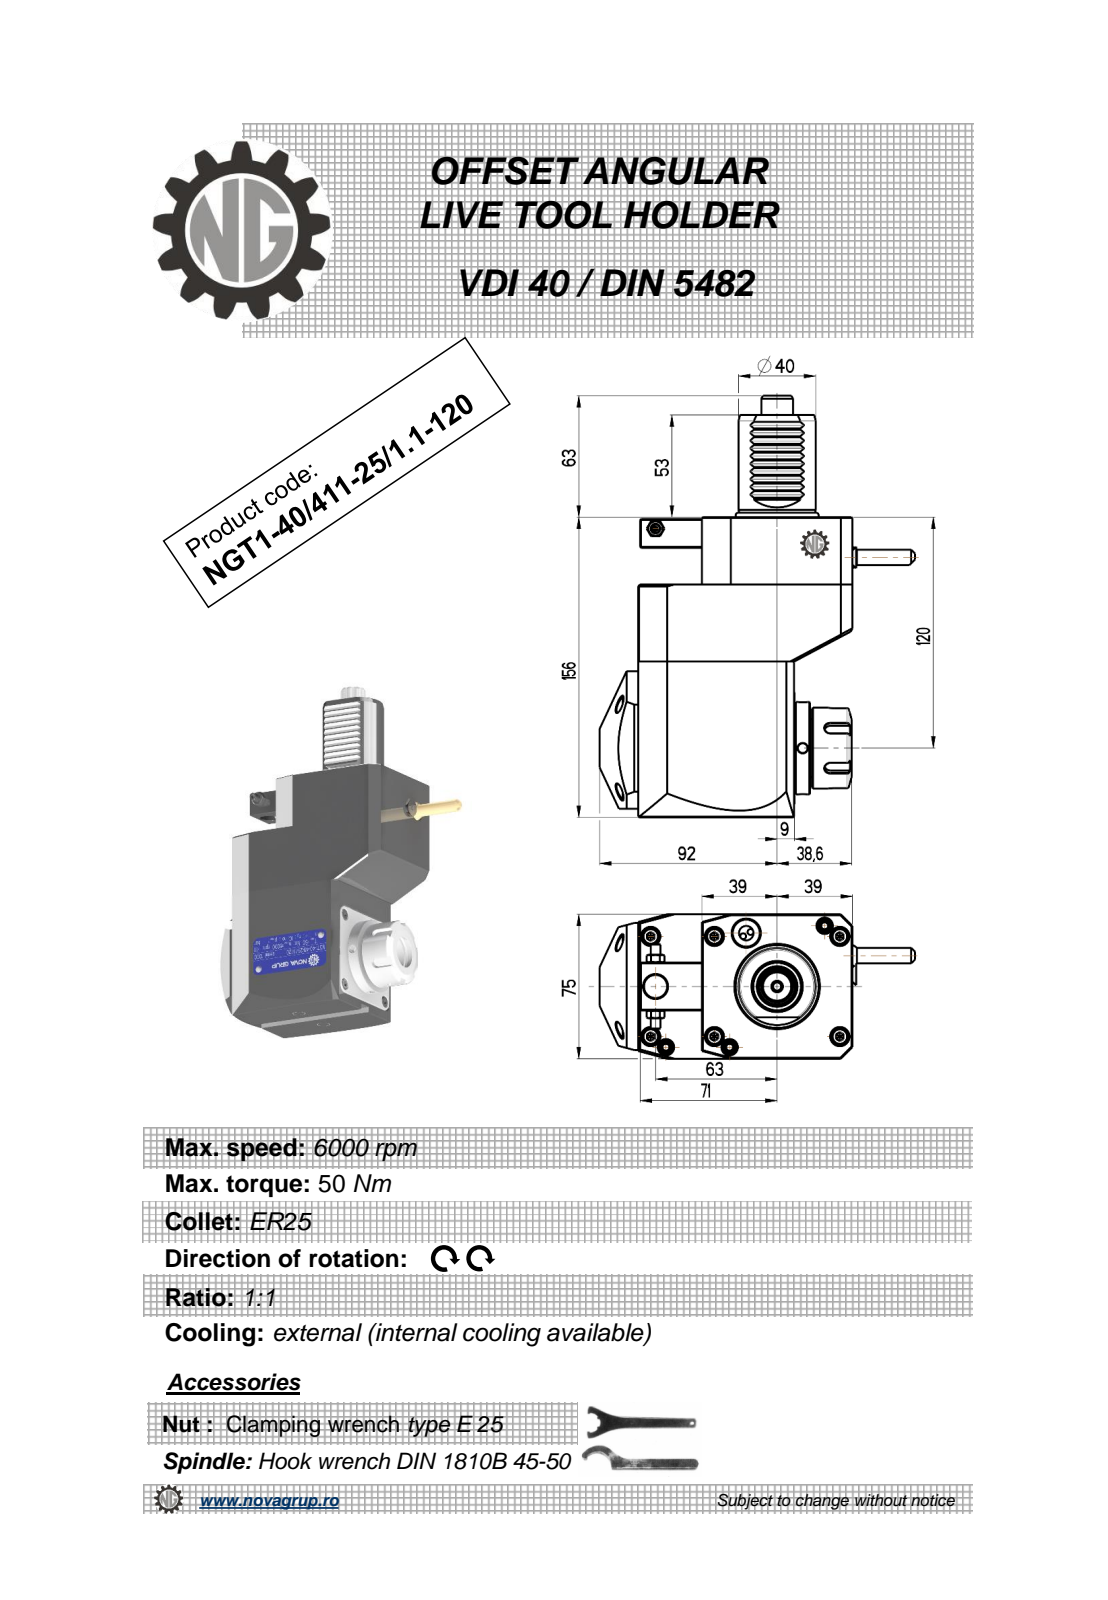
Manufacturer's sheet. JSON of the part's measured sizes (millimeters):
{"part_name": "NGT1_40_411_25_1_1_120", "step_written_by": "PRO/ENGINEER BY PARAMETRIC TECHNOLOGY CORPORATION, 2010280 (CONFIG_CONTROL_DESIGN)", "units": "millimeters", "bodies": {"solids": 1, "faces": 492, "planar": 202, "cylindrical": 124, "other": 166}, "overall_size": [219, 163.5, 76.6], "volume_mm3": 1164000, "surface_area_mm2": 86506, "round_holes": [[5, 3], [4.2, 2], [3, 1], [9.5, 1], [12, 1], [20.3, 1]], "round_bosses_or_shafts": [[48, 1], [42, 1], [40, 1], [37.5, 1], [33, 1], [11.2, 1], [8.96, 1], [8, 1]], "partial_cylinders_radius": [[3.03, 18], [0.26, 12], [0.3, 10], [0.22, 6], [3, 5], [0.5, 1], [6.75, 1], [8.22, 1]], "face_to_face_distances": [75, 156, 111, 30, 35, 121, 81, 33, 48, 78], "hole_center_spacings": [13.25, 20.93, 63, 76.25, 100.28, 112.5, 137.15]}
